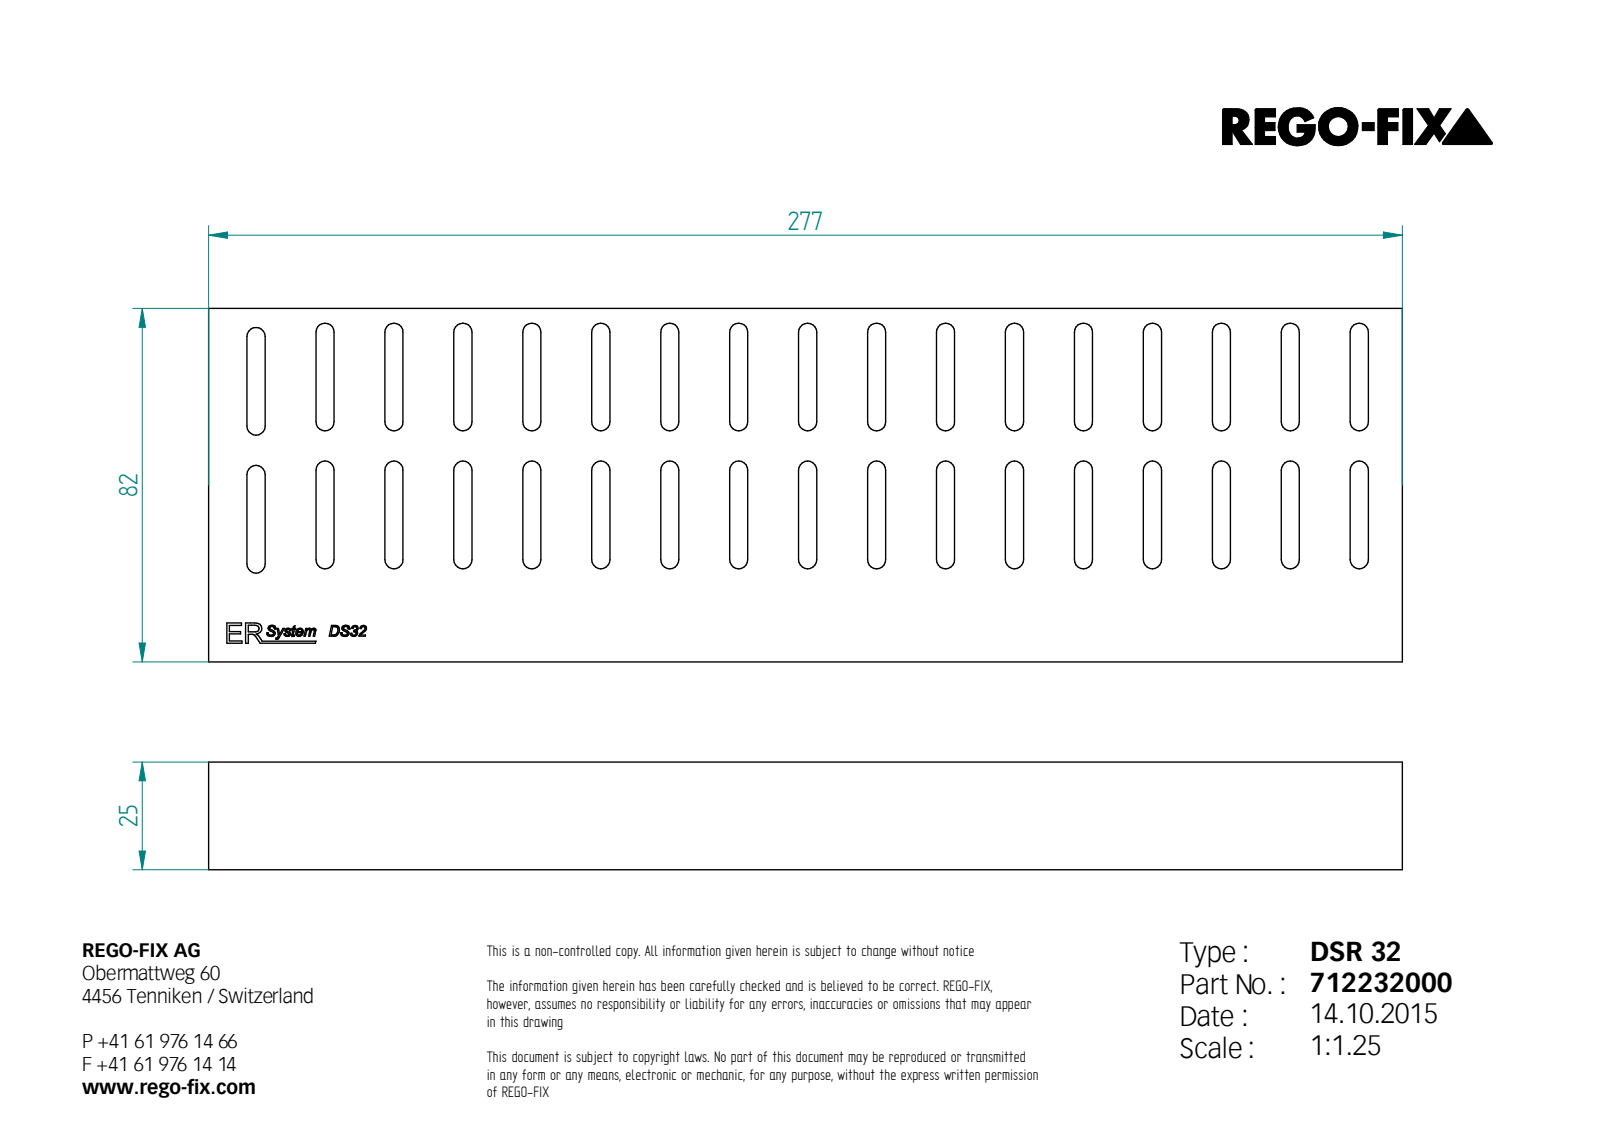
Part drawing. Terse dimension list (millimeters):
written by: Unknown (AUTOMOTIVE_DESIGN)
unit: mm
bodies: 1 solid, 279 faces (181 planar, 68 cylindrical, 30 other)
size: 277 × 82 × 25
volume: 540 316 mm³; area: 78 321 mm²
rounds: 68× R2.1
face distances: 25, 82, 16, 32, 17, 8, 48, 4.2, 64, 20.2
